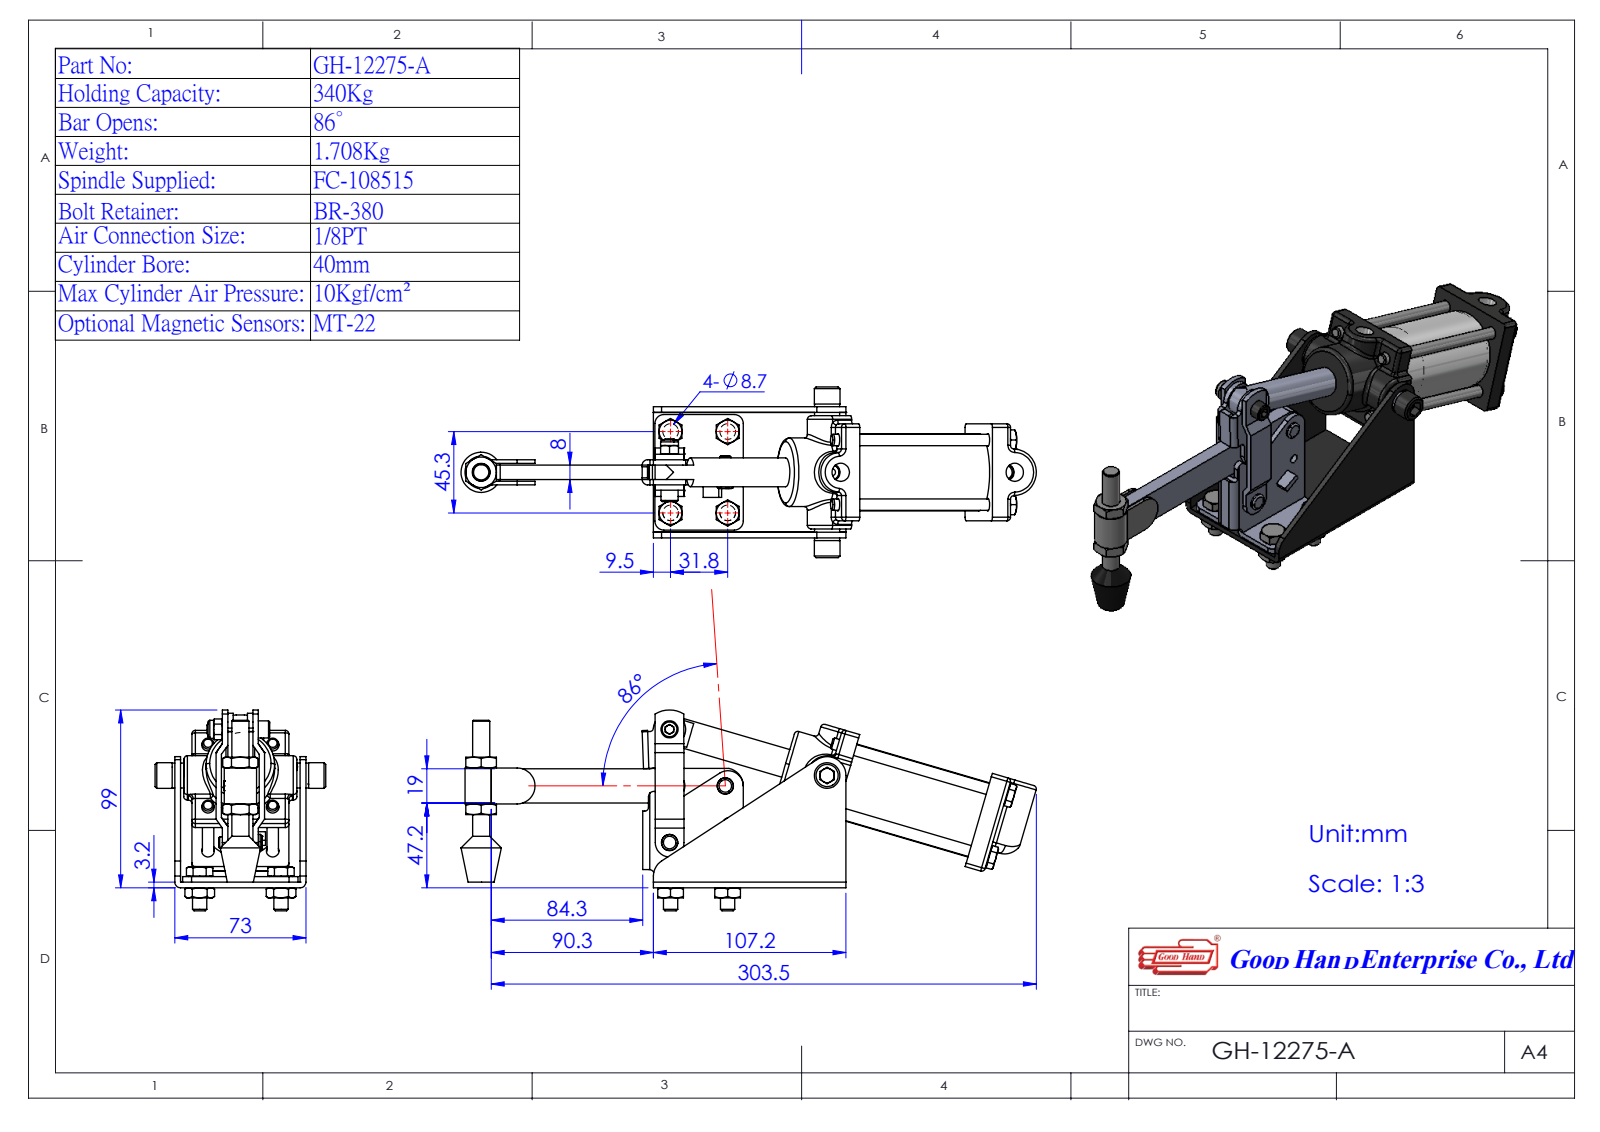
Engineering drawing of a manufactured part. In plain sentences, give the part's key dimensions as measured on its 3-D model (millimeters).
The part is named "Group4^GH-12275-A(簡化); 112275A08-1^GH-12275-A(簡化); Group7^GH-12275-A(簡化); 12265A-CYLINDER-1^GH-12275-A(簡化) (+4 more)". Its 3-D file was written by "SolidWorks 2016 (AUTOMOTIVE_DESIGN)". It is 7 solids with 842 faces: 348 planar, 235 cylindrical and 259 other. Overall it measures 320.36 by 111.85 by 85.65 millimeters. Its volume is 317 355 cubic millimeters and its surface area 142 521 square millimeters. Round holes: 4 of diameter 5.5, 2 of diameter 7.9, 1 of diameter 4.8, 1 of diameter 16, 1 of diameter 42. Round bosses or shafts: 5 of diameter 7.94, 4 of diameter 12.7, 4 of diameter 6.35, 2 of diameter 11.13, 1 of diameter 43, 1 of diameter 42, 1 of diameter 38.2, 1 of diameter 16. Partial cylindrical surfaces (rounded edges, fillets, slot ends): 36 of radius 2, 8 of radius 5, 4 of radius 1, 3 of radius 3, 3 of radius 10, 2 of radius 2.02, 2 of radius 3.21, 2 of radius 4. The main face-to-face distances are 3.2, 3, 40.5, 11, 32.5, 69.8, 29.3, 37.3, 43.5, 29.5. The hole center spacings are 31.52, 30, 44.2, 44.24, 57, 63, 86.89, 91.45.
